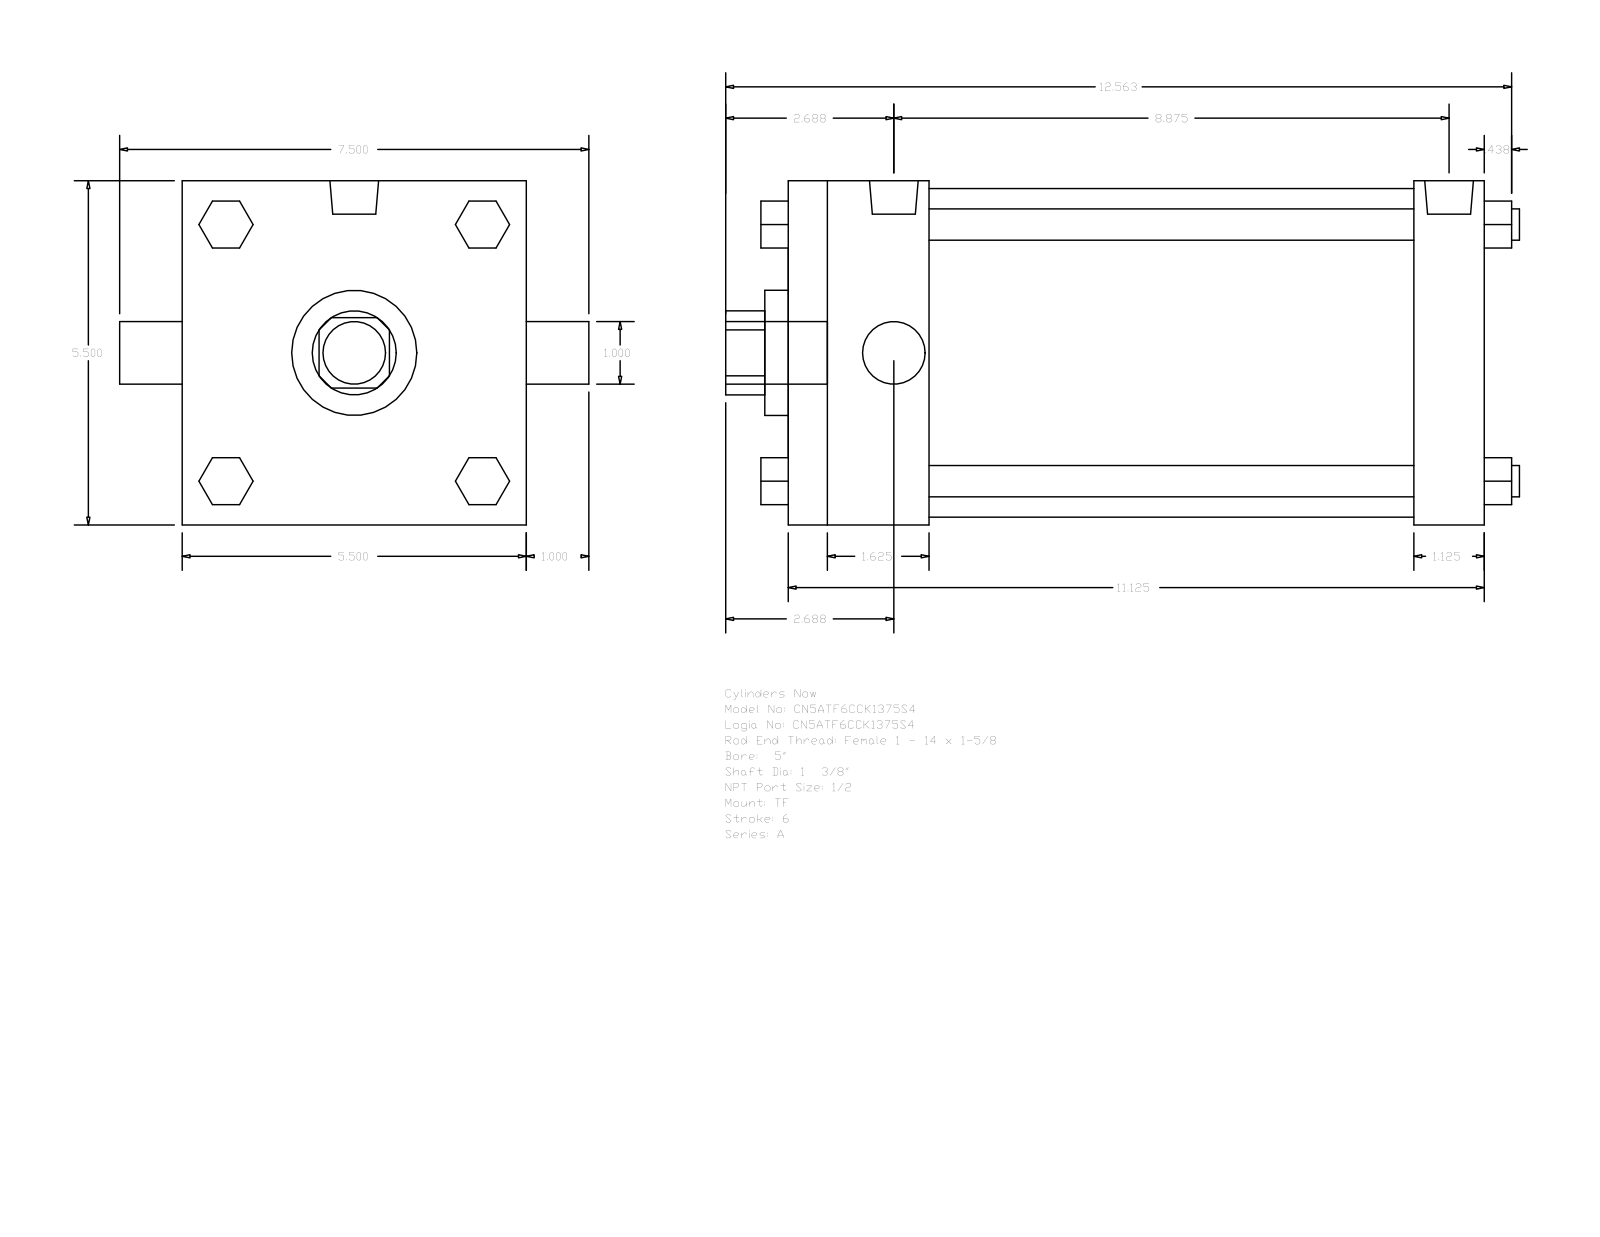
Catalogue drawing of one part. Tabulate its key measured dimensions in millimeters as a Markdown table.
| quantity | value |
| --- | --- |
| part name | A_TF__0500_1.375 |
| STEP written by | GSSL Pune (CONFIG_CONTROL_DESIGN) |
| units | millimeters |
| bodies | 0 solids, 120 faces (92 planar, 28 cylindrical, 0 other) |
| overall size | 322.26 × 190.5 × 139.7 |
| round holes (diameter × count) | 25.4 × 1, 34.92 × 1, 50.8 × 1, 133.35 × 1 |
| round bosses / shafts (diameter × count) | 12.7 × 4, 8.73 × 3, 19.77 × 2, 25.4 × 1 |
| partial cylindrical surfaces (radius × count) | 17.06 × 1 |
| main face-to-face distances | 139.7, 282.58, 28.58, 254, 57.15, 196.85, 225.43, 19.05, 52.07, 90.18 |
